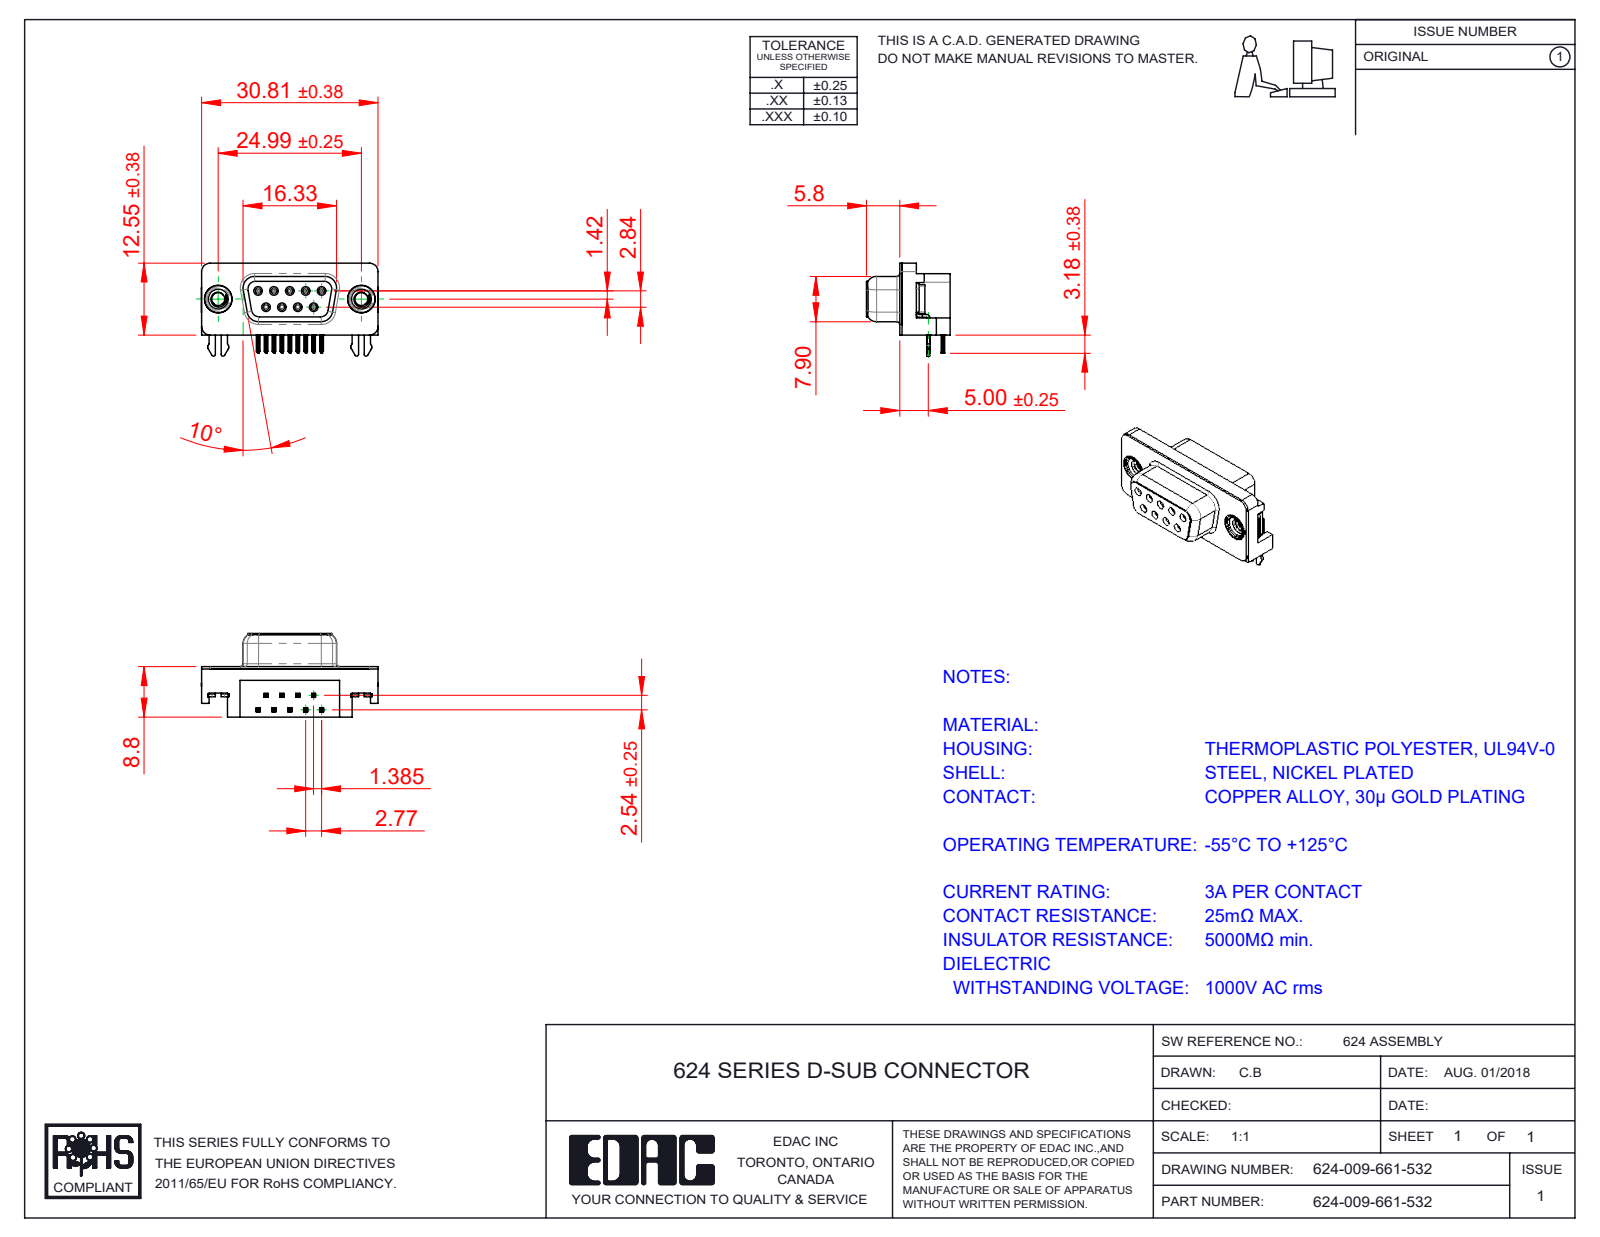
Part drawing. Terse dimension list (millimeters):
name: 624-009-661-532; 624 2 Prong Board Lock; 624 Housing_9 Socket; 624 Shell_9 Socket (+3 more)
written by: SolidWorks 2016 (CONFIG_CONTROL_DESIGN)
unit: mm
bodies: 15 solids, 1552 faces (670 planar, 410 cylindrical, 472 other)
size: 30.89 × 16.25 × 14.6
volume: 2 947 mm³; area: 4 397 mm²
holes: 9× ⌀0.8, 9× ⌀0.9, 2× ⌀2.26, 2× ⌀4, 2× ⌀4.8, 2× ⌀5
bosses: 9× ⌀1.2, 2× ⌀4.9, 2× ⌀4.75, 2× ⌀3.9
rounds: 72× R0.1, 36× R0.15, 18× R0.35, 10× R0.5, 10× R1, 9× R0.34, 8× R0.25, 8× R1.35
face distances: 0.4, 8.4, 8.8, 2.9, 2.5, 6.2, 5.9, 0.35, 0.85, 10.69
hole spacings: 3.16, 2.77, 5.54, 5.03, 5.04, 8.31, 7.48, 7.49
